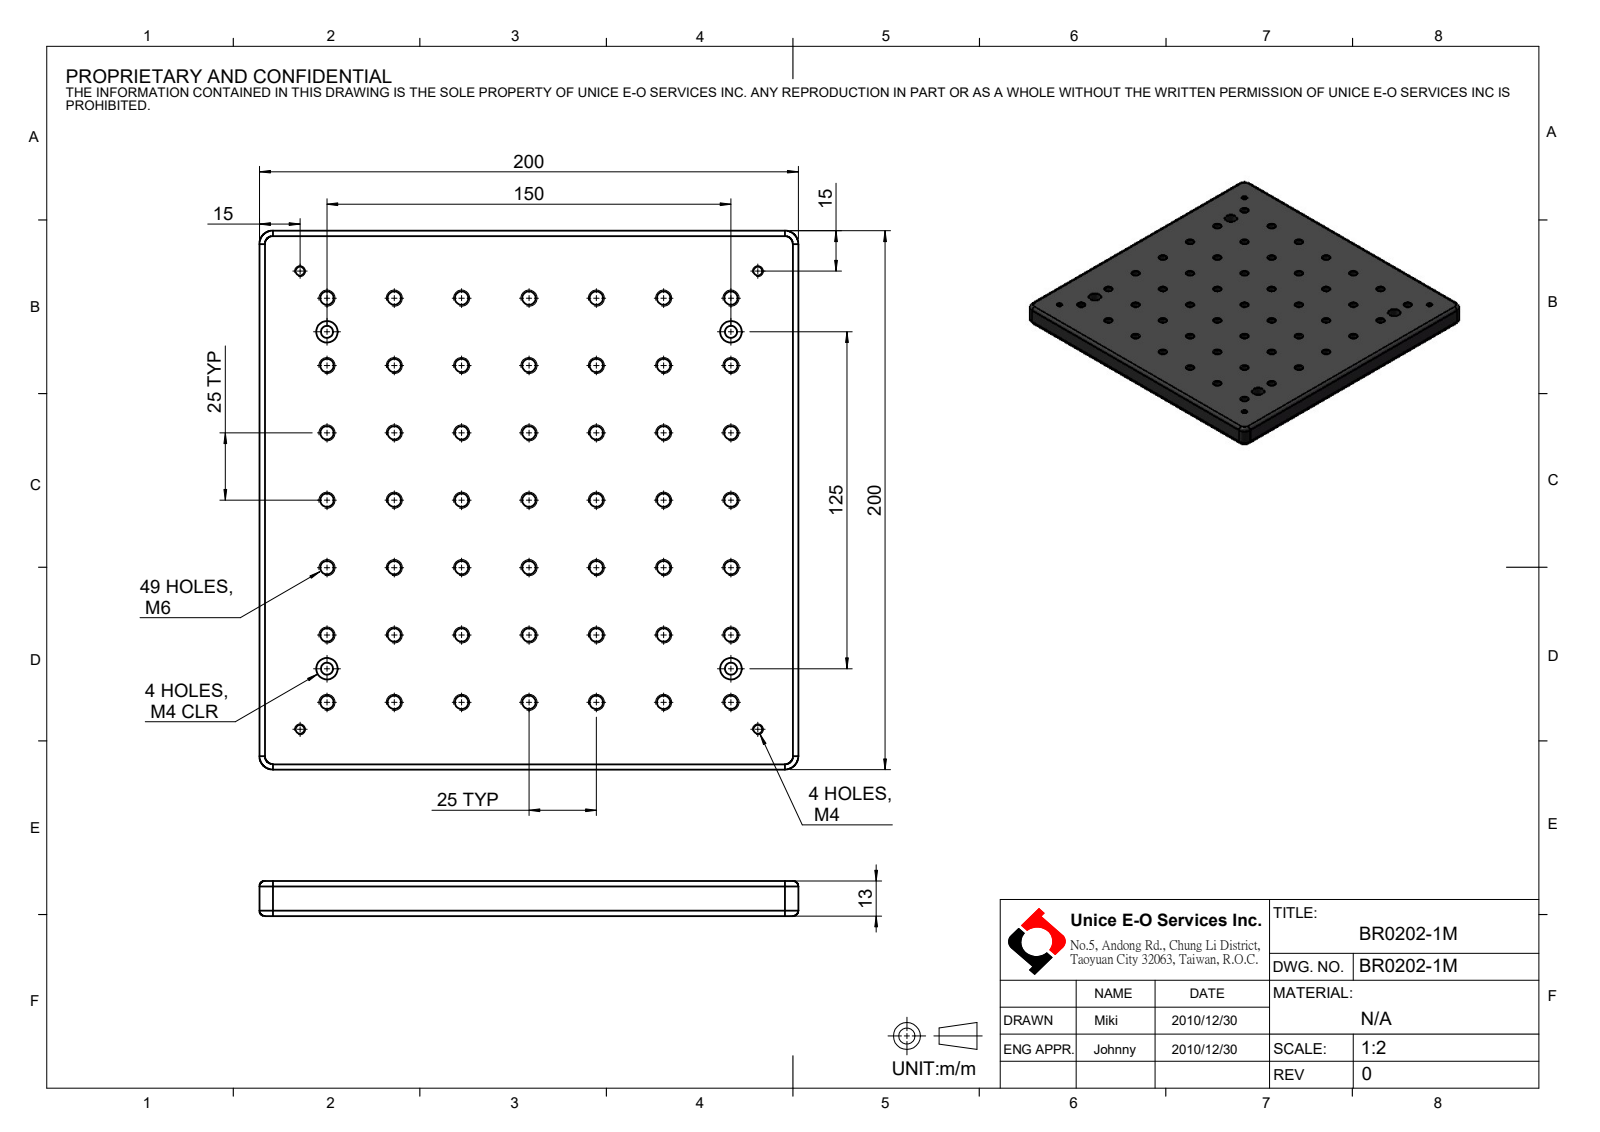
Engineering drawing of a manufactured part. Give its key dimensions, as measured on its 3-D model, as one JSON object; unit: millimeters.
{"part_name": "BR0202-1M", "step_written_by": "SolidWorks 2016 (CONFIG_CONTROL_DESIGN)", "units": "millimeters", "bodies": {"solids": 1, "faces": 152, "planar": 10, "cylindrical": 134, "other": 8}, "overall_size": [200, 200, 13], "volume_mm3": 503763, "surface_area_mm2": 98307, "round_holes": [[5, 49], [3.3, 4], [4.5, 4], [8, 4]], "partial_cylinders_radius": [[2, 8], [5, 4]], "face_to_face_distances": [13, 200, 7, 6], "hole_center_spacings": [25, 152.07, 50, 158.11, 125, 75, 150, 167.71]}
